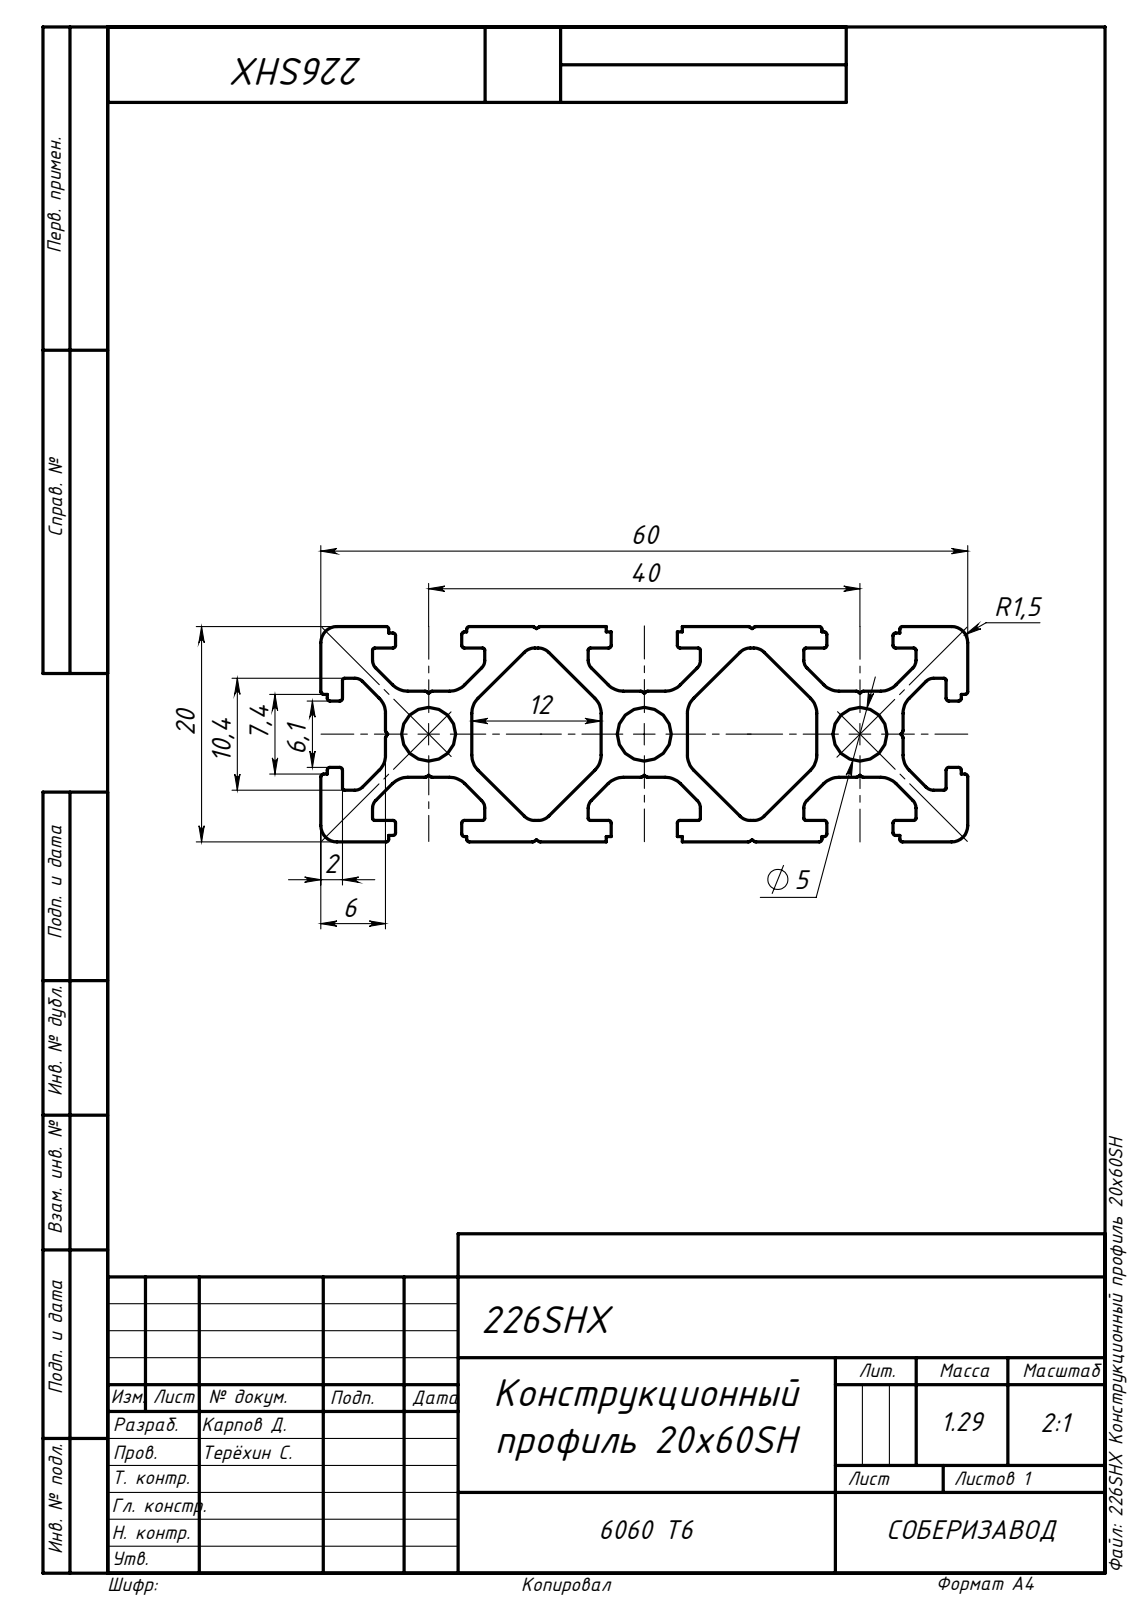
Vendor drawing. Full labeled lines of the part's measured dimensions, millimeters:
STEP written by: SolidWorks 2019 (AUTOMOTIVE_DESIGN)
Units: millimetres
Bodies: 1 solid, 308 faces (170 planar, 138 cylindrical, 0 other)
Overall size (bounding box): 1000 × 60 × 20
Volume: 478 959 mm³ · Surface area: 426 755 mm²
Round holes (diameter × count): ⌀5 ×3
Partial cylindrical surfaces — rounded edges, fillets, slot ends (radius × count): R0.25 ×64, R2 ×24, R0.2 ×16, R1 ×16, R1.4 ×8, R1.5 ×4
Main face-to-face distances: 20, 12, 2, 14, 6, 4, 1.74, 12.36, 14.1, 18
Hole centre spacings: 20, 40
